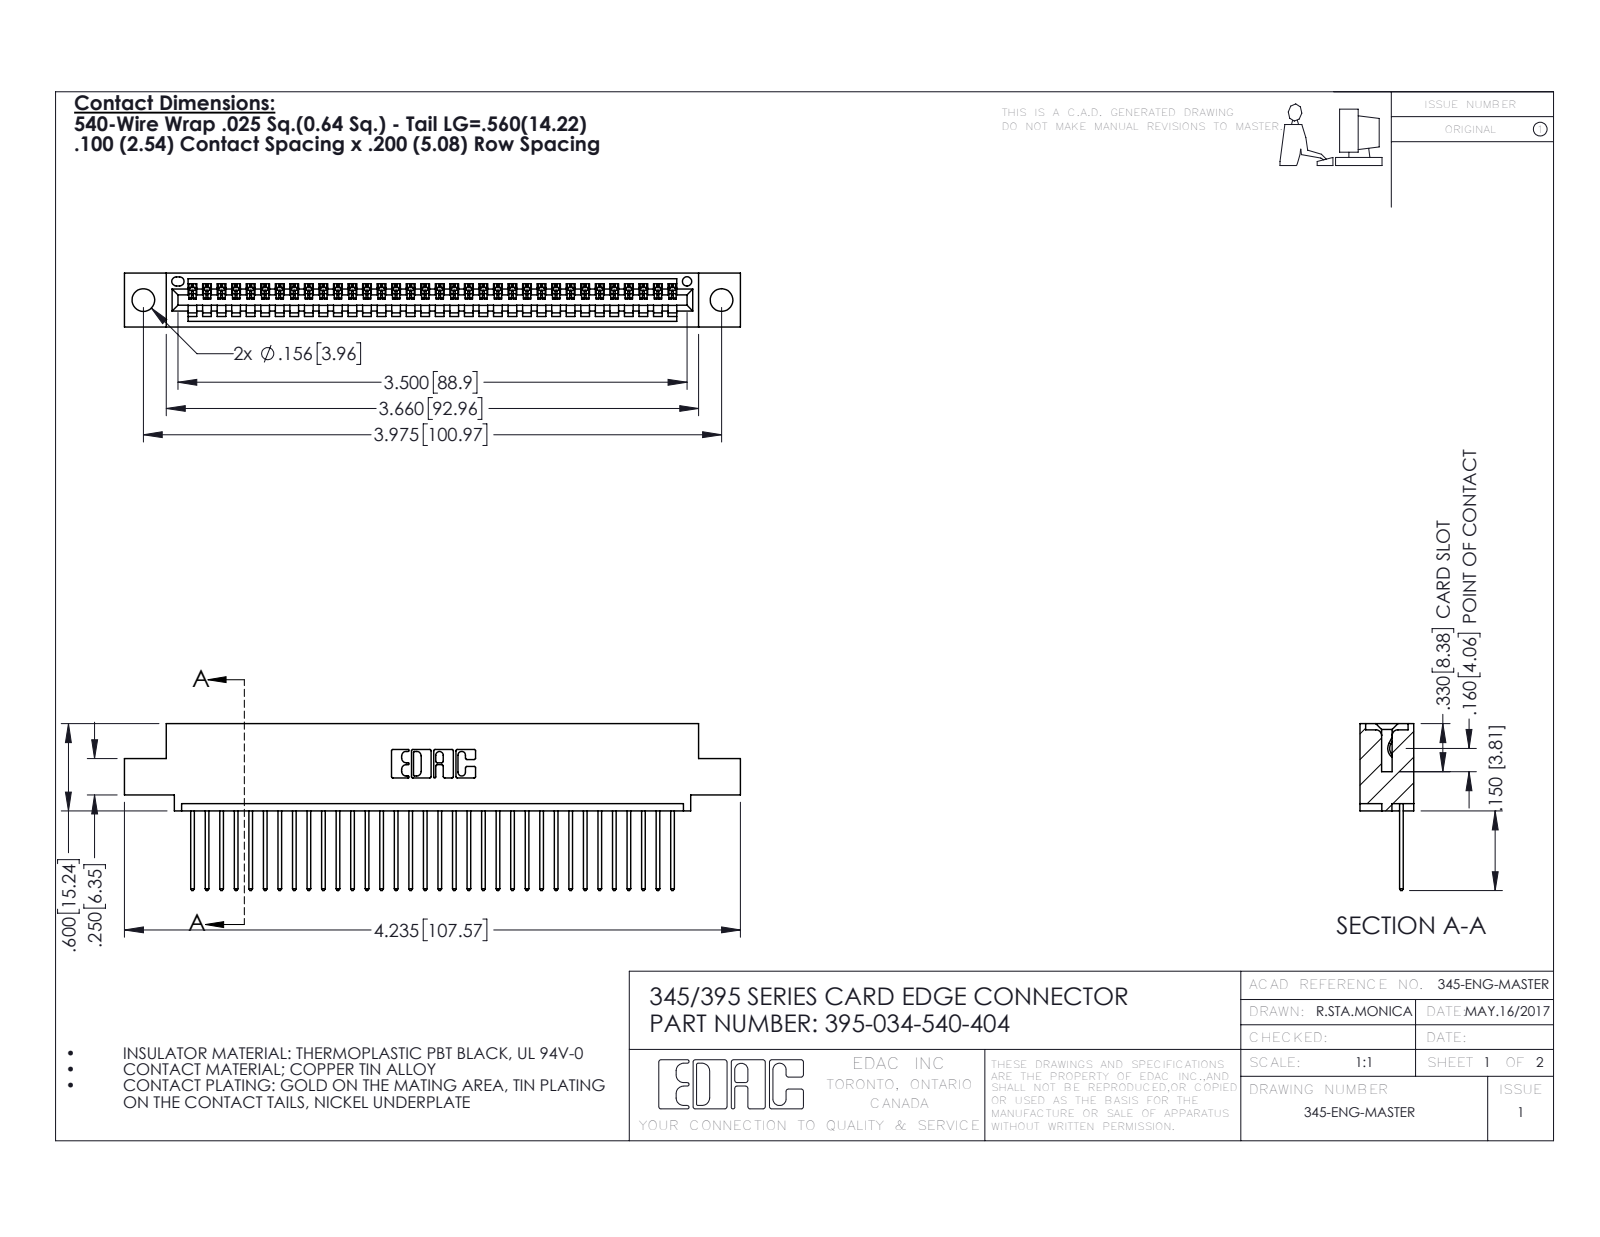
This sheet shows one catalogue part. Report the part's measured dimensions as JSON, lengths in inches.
{"part_name": "395-034-540-404; 345-292-001_345-293-140; 345 Part_0.110 Offset - 0.156 Dia-TH", "step_written_by": "SolidWorks 2016 (CONFIG_CONTROL_DESIGN)", "units": "inches", "bodies": {"solids": 35, "faces": 2102, "planar": 1444, "cylindrical": 658, "other": 0}, "overall_size": [4.235, 1.147, 0.37], "volume_in3": 0.612, "surface_area_in2": 20.85, "round_holes": [[0.156, 2], [0.064, 1]], "partial_cylinders_radius": [[0.006, 68], [0.01, 68], [0.01, 22], [0.007, 6], [0.031, 6], [0.026, 3], [0.031, 2], [0.04, 2]], "face_to_face_distances": [0.298, 0.072, 0.37, 0.2, 0.098, 0.272, 0.025, 0.225, 0.149, 0.072], "hole_center_spacings": [0.27, 3.74, 3.975]}
